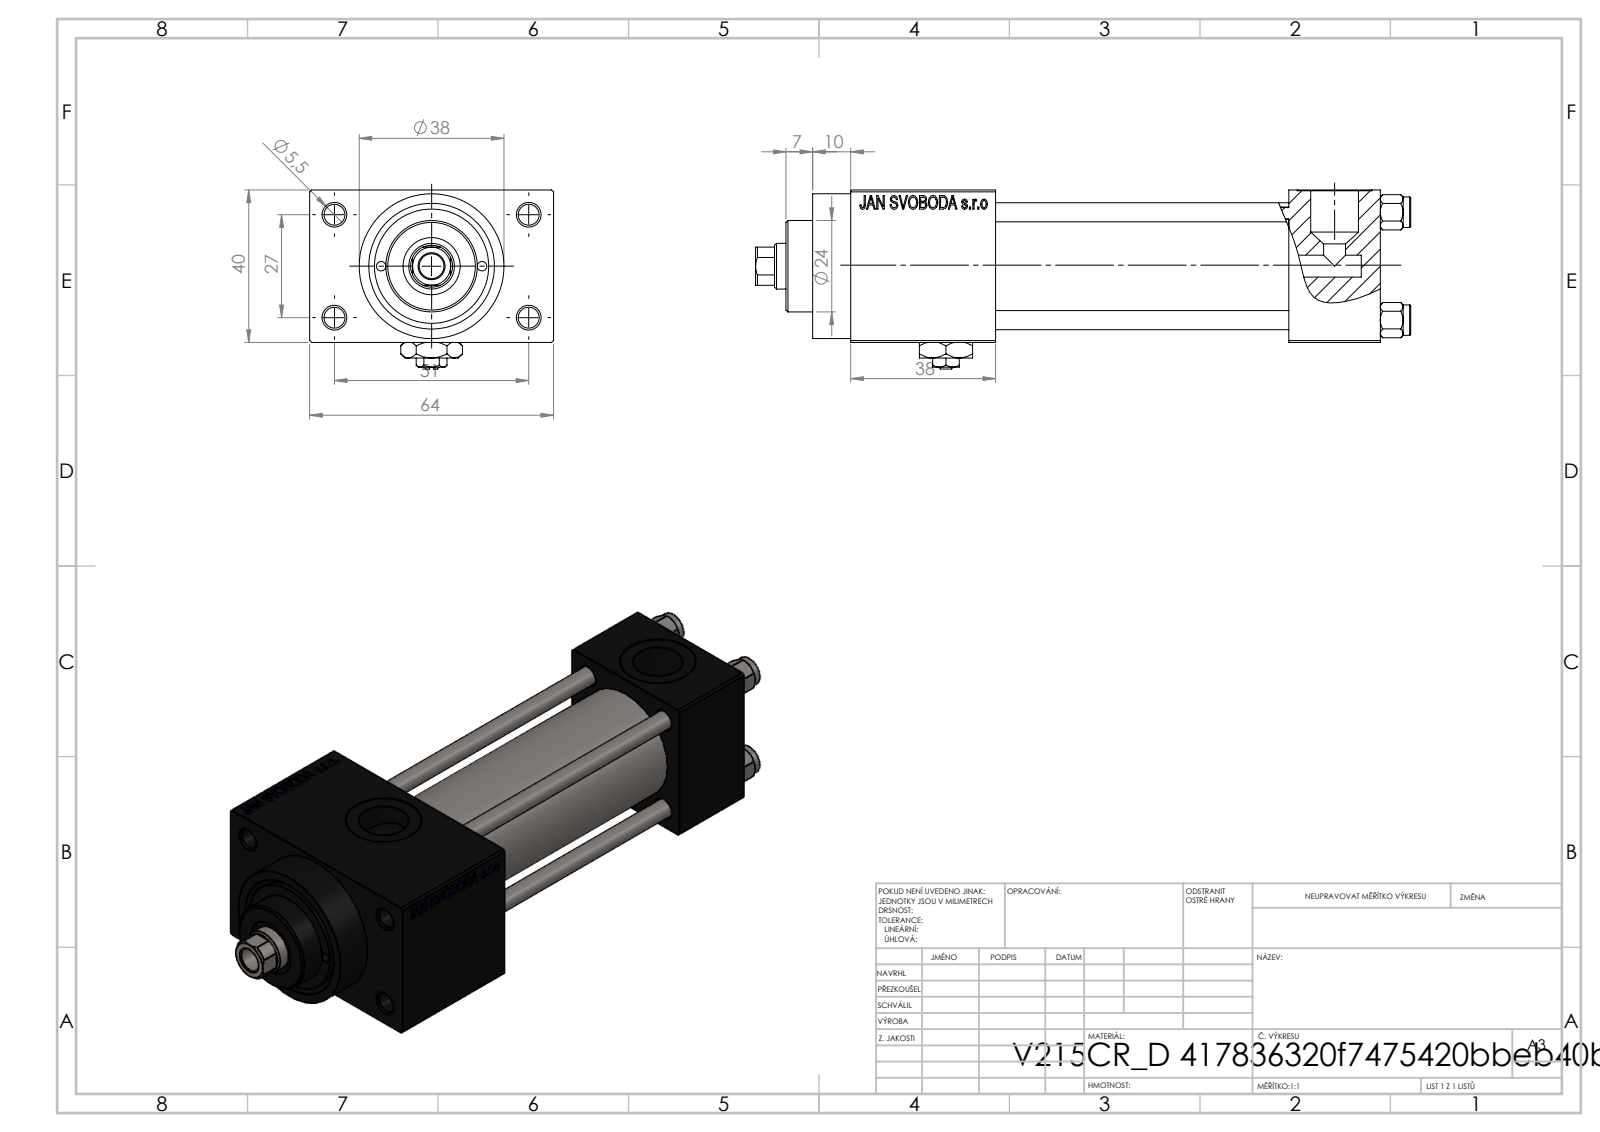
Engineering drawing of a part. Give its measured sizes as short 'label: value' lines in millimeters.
name: V215CR_VCP_D; NUT_M5_D; V215CR_D_TYCINKA; Zatka_pro_OIL_PORT (+2 more)
written by: SolidWorks 2019 (CONFIG_CONTROL_DESIGN)
unit: mm
bodies: 12 solids, 1158 faces (521 planar, 97 cylindrical, 540 other)
size: 172 × 64 × 47
volume: 188 796 mm³; area: 70 519 mm²
holes: 4× ⌀5, 4× ⌀5.5, 3× ⌀20, 2× ⌀2.5, 2× ⌀7, 2× ⌀13.16, 1× ⌀6.5, 1× ⌀12, 1× ⌀15, 1× ⌀25, 1× ⌀30
bosses: 4× ⌀8, 1× ⌀38, 1× ⌀31, 1× ⌀24
rounds: 1× R5.5
face distances: 40, 12, 52, 77, 24, 101, 64, 38, 115, 139
hole spacings: 11.37, 14.18, 18.23, 20.01, 28.3, 28.85, 29.89, 30.84
